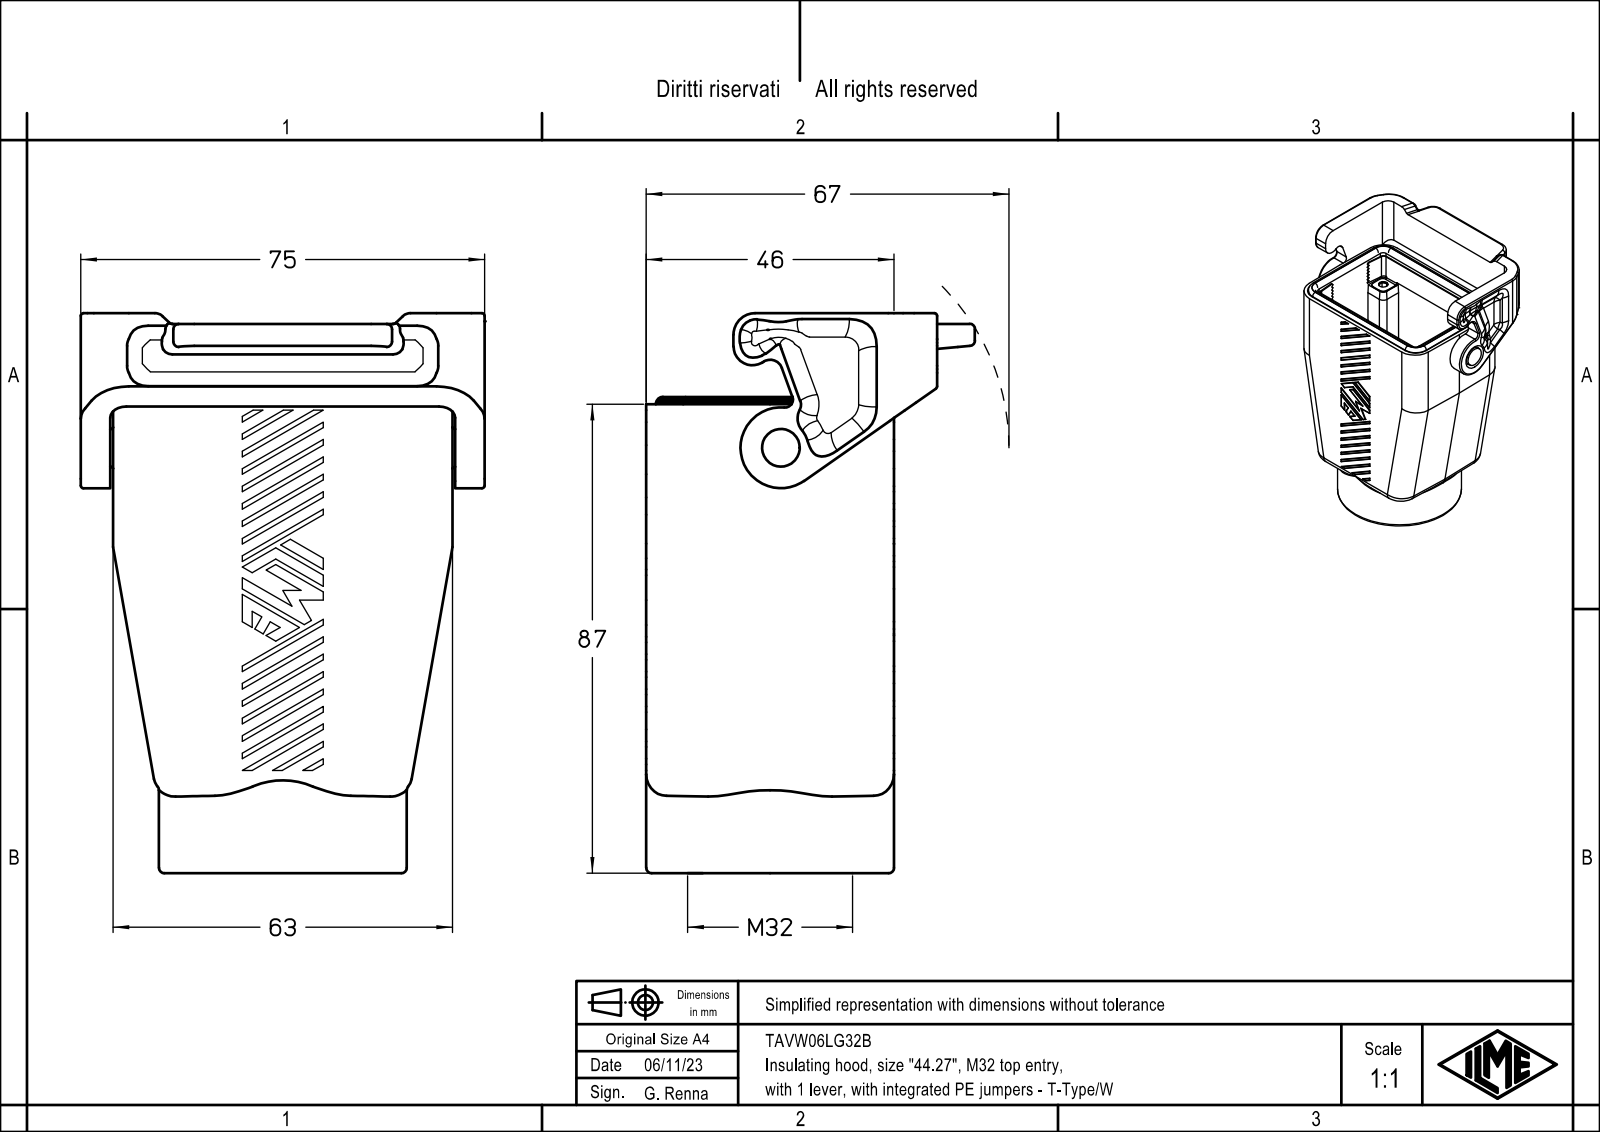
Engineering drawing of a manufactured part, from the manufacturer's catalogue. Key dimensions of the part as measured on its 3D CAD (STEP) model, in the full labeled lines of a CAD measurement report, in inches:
Part name (STEP PRODUCT): TAVW06LG32B
STEP written by: Creo Elements/Direct Modeling 20.1B 02-Apr-2019 (C) Parametric Technology GmbH (AUTOMOTIVE_DESIGN)
Units: inches
Bodies: 1 solid, 708 faces (312 planar, 344 cylindrical, 52 other)
Overall size (bounding box): 4.091 × 2.953 × 2.407
Volume: 6.772 in³ · Surface area: 66.72 in²
Round holes (diameter × count): ⌀0.138 ×4, ⌀1.102 ×1, ⌀1.205 ×1
Round bosses / shafts (diameter × count): ⌀1.811 ×1, ⌀0.276 ×1
Partial cylindrical surfaces — rounded edges, fillets, slot ends (radius × count): R0.006 ×128, R0.059 ×15, R0.079 ×14, R0.118 ×13, R0.051 ×12, R0.039 ×8, R0.276 ×8, R0.063 ×4
Main face-to-face distances: 0.213, 1.598, 1.811, 1.386, 0.232, 2.287, 0.118, 0.331, 1.929, 1.717
Hole centre spacings: 1.016, 1.063, 1.732, 2.032
